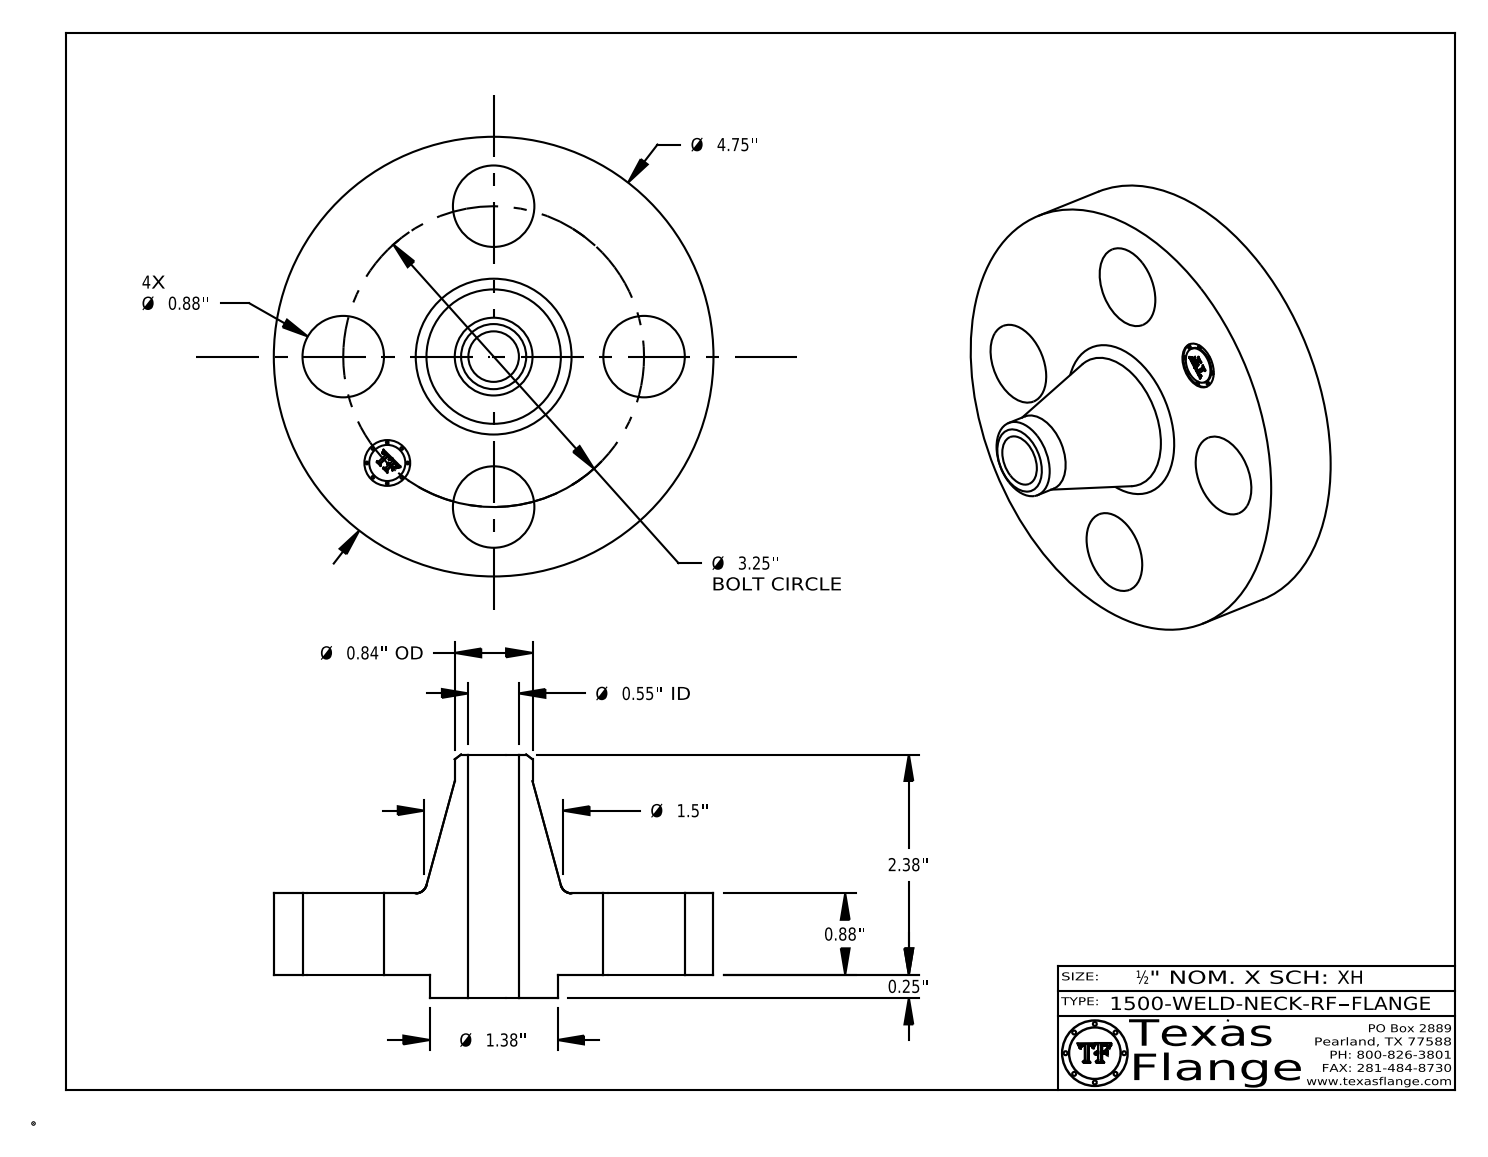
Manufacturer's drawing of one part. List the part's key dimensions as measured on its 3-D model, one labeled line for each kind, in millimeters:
Part name (STEP PRODUCT): 1500-WELD-NECK-RF
STEP written by: CATIA V5 STEP AP214 (AUTOMOTIVE_DESIGN)
Units: millimetres
Bodies: 1 solid, 411 faces (369 planar, 36 cylindrical, 6 other)
Overall size (bounding box): 120.7 × 120.7 × 66.8
Volume: 241 100 mm³ · Surface area: 40 390 mm²
Round holes (diameter × count): ⌀22.4 ×4, ⌀12.6 ×1, ⌀13.9 ×1
Round bosses / shafts (diameter × count): ⌀0.8 ×8, ⌀120.7 ×1, ⌀35.1 ×1, ⌀21.3 ×1, ⌀9.9 ×1
Main face-to-face distances: 22.4, 6.4, 28.7, 66.8, 60.5, 38.1, 28.3, 22, 0.4, 38.5
Hole centre spacings: 41.3, 58.4, 31.6, 76.3, 82.6
